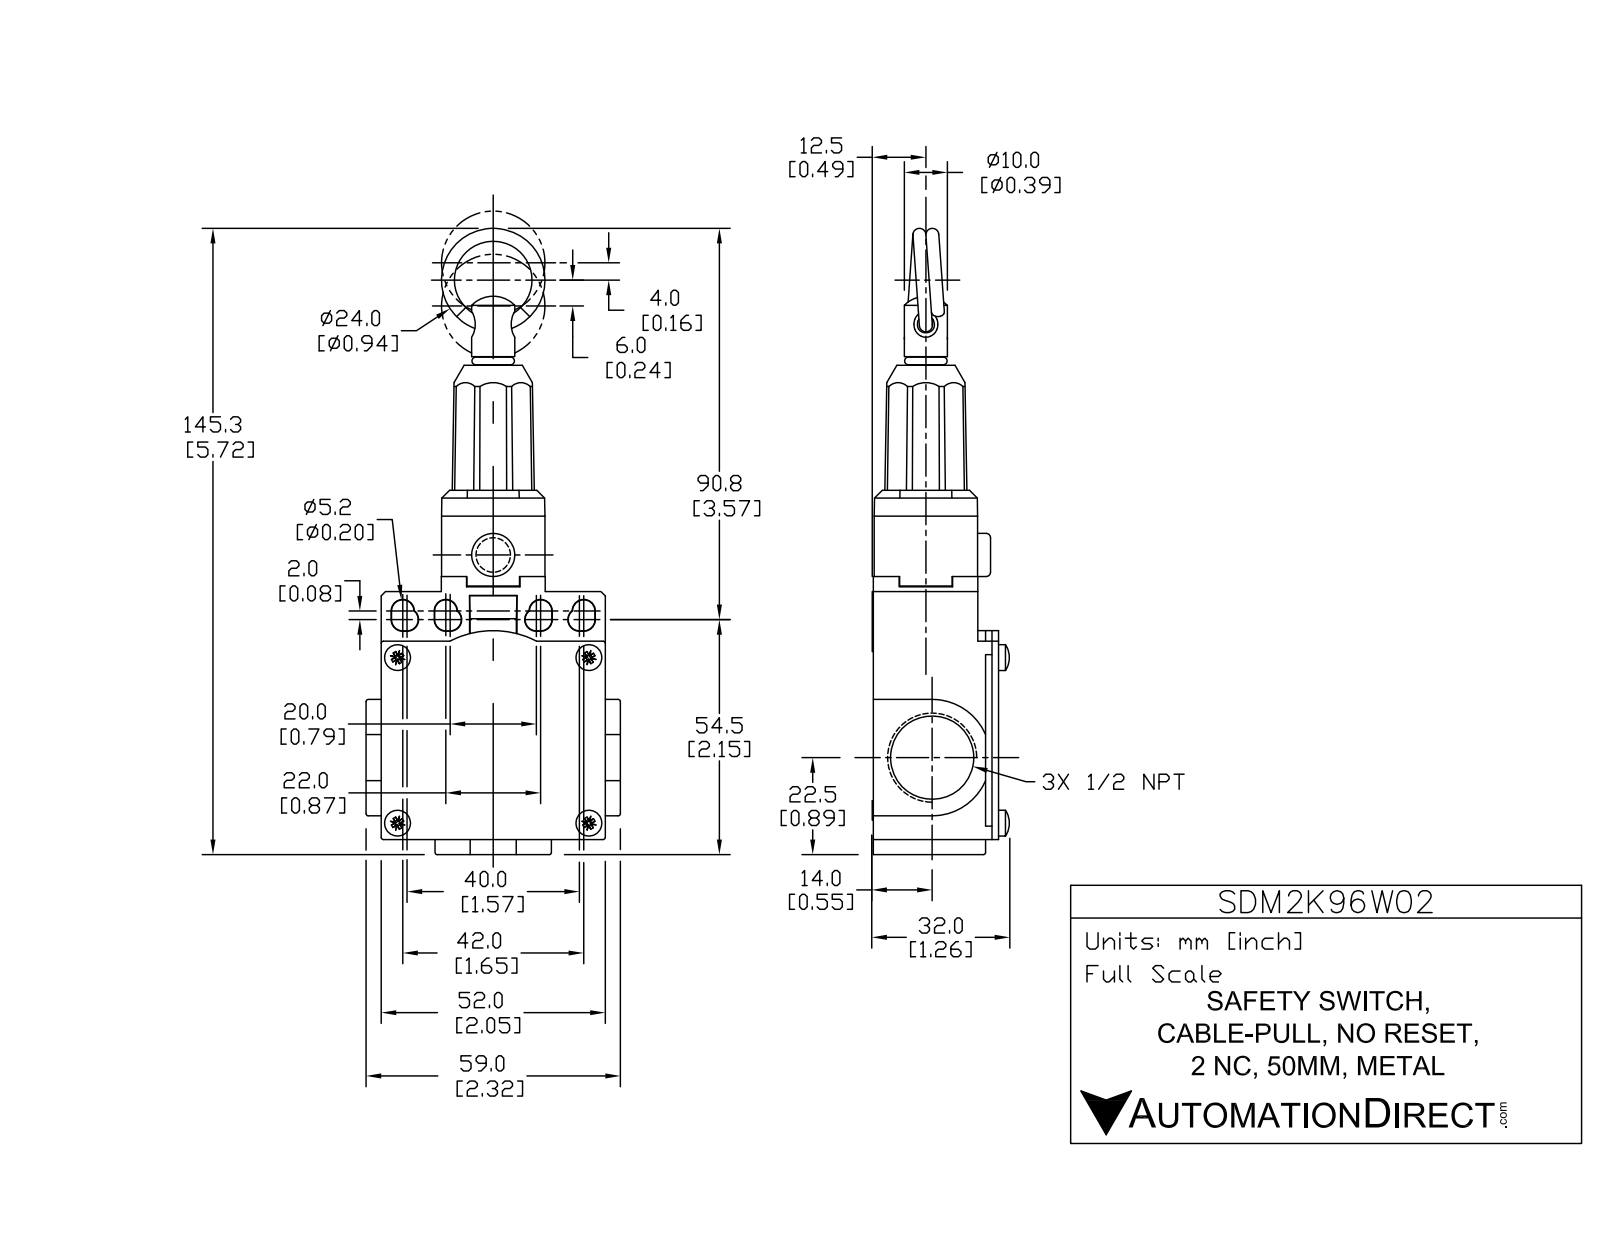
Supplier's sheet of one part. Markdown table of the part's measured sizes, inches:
| quantity | value |
| --- | --- |
| part name | SDM2K96W02 |
| STEP written by | SolidWorks 2017 (AUTOMOTIVE_DESIGN) |
| units | inches |
| bodies | 5 solids, 237 faces (109 planar, 95 cylindrical, 33 other) |
| overall size | 5.768 × 2.323 × 1.252 |
| volume | 6.41 in³ |
| surface area | 39.57 in² |
| round holes (diameter × count) | 0.669 × 2, 0.748 × 2, 0.157 × 1, 0.398 × 1, 0.591 × 1 |
| round bosses / shafts (diameter × count) | 0.22 × 4, 0.217 × 4, 0.394 × 2, 0.248 × 1 |
| partial cylindrical surfaces (radius × count) | 0.102 × 12, 0.02 × 10, 0.118 × 4, 0.531 × 2, 0.394 × 1, 0.4 × 1, 0.866 × 1 |
| main face-to-face distances | 1.144, 0.138, 0.551, 0.945, 0.098, 1.496, 0.236, 2.047, 0.199, 1.398 |
| hole center spacings | 0.069, 3.997 |
